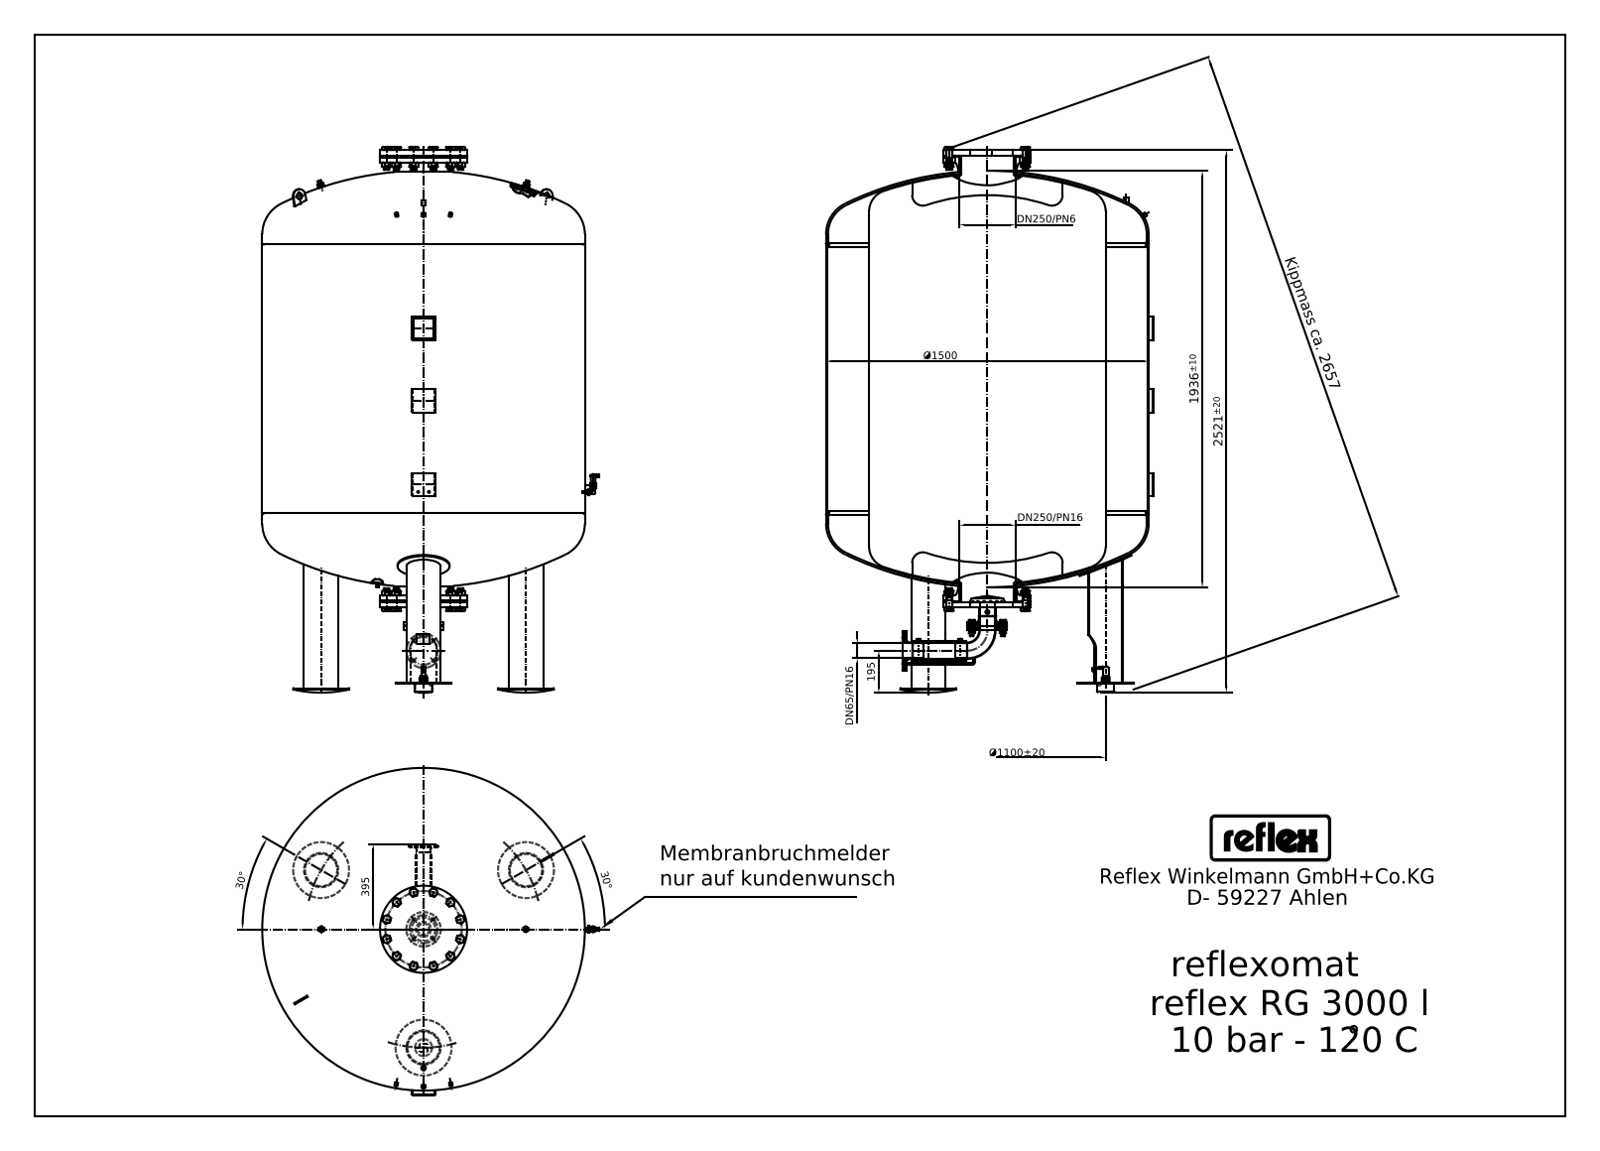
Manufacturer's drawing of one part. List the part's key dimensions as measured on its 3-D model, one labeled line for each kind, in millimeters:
STEP written by: Mechanical Desktop 2009 (CONFIG_CONTROL_DESIGN)
Units: millimetres
Bodies: 33 solids, 1142 faces (640 planar, 270 cylindrical, 232 other)
Overall size (bounding box): 2516 × 1566 × 1520
Volume: 3 106 000 000 mm³ · Surface area: 20 830 000 mm²
Round holes (diameter × count): ⌀9 ×2, ⌀11.45 ×2, ⌀3.5 ×1, ⌀8 ×1, ⌀14.95 ×1, ⌀20 ×1, ⌀30 ×1, ⌀150 ×1, ⌀260.4 ×1
Round bosses / shafts (diameter × count): ⌀16 ×12, ⌀12 ×4, ⌀159 ×3, ⌀21.3 ×3, ⌀18.5 ×3, ⌀76.1 ×2, ⌀28 ×2, ⌀20 ×2
Partial cylindrical surfaces — rounded edges, fillets, slot ends (radius × count): R2 ×10, R1 ×5, R8.44 ×4, R3.38 ×3, R6 ×3, R3 ×2, R5.76 ×2, R10.12 ×2
Main face-to-face distances: 1276, 22, 2071, 27, 2044, 384, 1665, 389, 1687, 411
Hole centre spacings: 820.38, 50, 95, 550, 645, 769.5, 945.85, 1004.07
